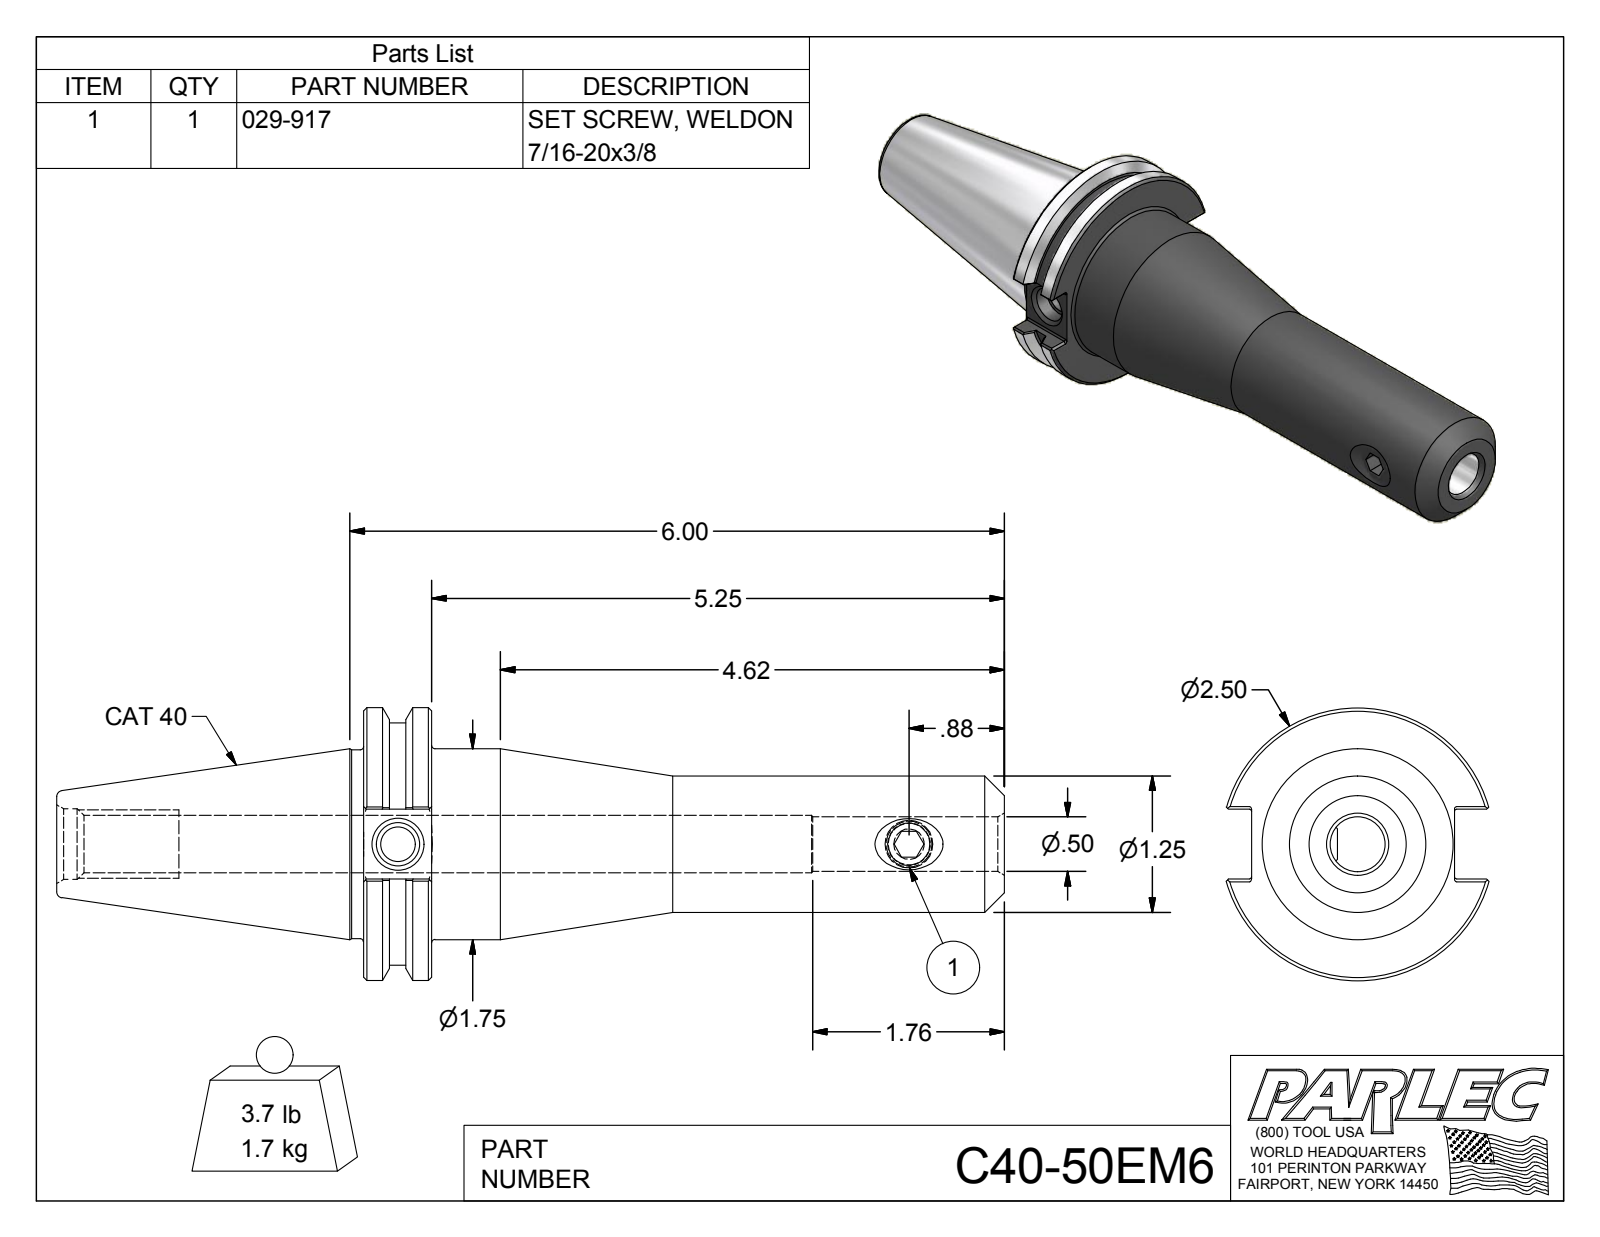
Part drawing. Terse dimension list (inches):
name: C40-50EM6; C40-50EM6-1; 029-917
written by: Autodesk Inventor 2012 (AUTOMOTIVE_DESIGN)
unit: in
bodies: 2 solids, 100 faces (40 planar, 28 cylindrical, 32 other)
size: 8.687 × 2.5 × 2.406
volume: 13.01 in³; area: 62.24 in²
holes: 1× ⌀0.315, 1× ⌀0.383, 1× ⌀0.399, 1× ⌀0.5, 1× ⌀0.527, 1× ⌀0.648
bosses: 1× ⌀2.5, 1× ⌀2.219, 1× ⌀1.75, 1× ⌀1.73, 1× ⌀1.25, 1× ⌀0.437
rounds: 12× R0.02
face distances: 0.625, 5.875, 5.25, 0.236, 0.64, 1.86, 2.812, 3.437, 8.687, 3.201
hole spacings: 4.685
